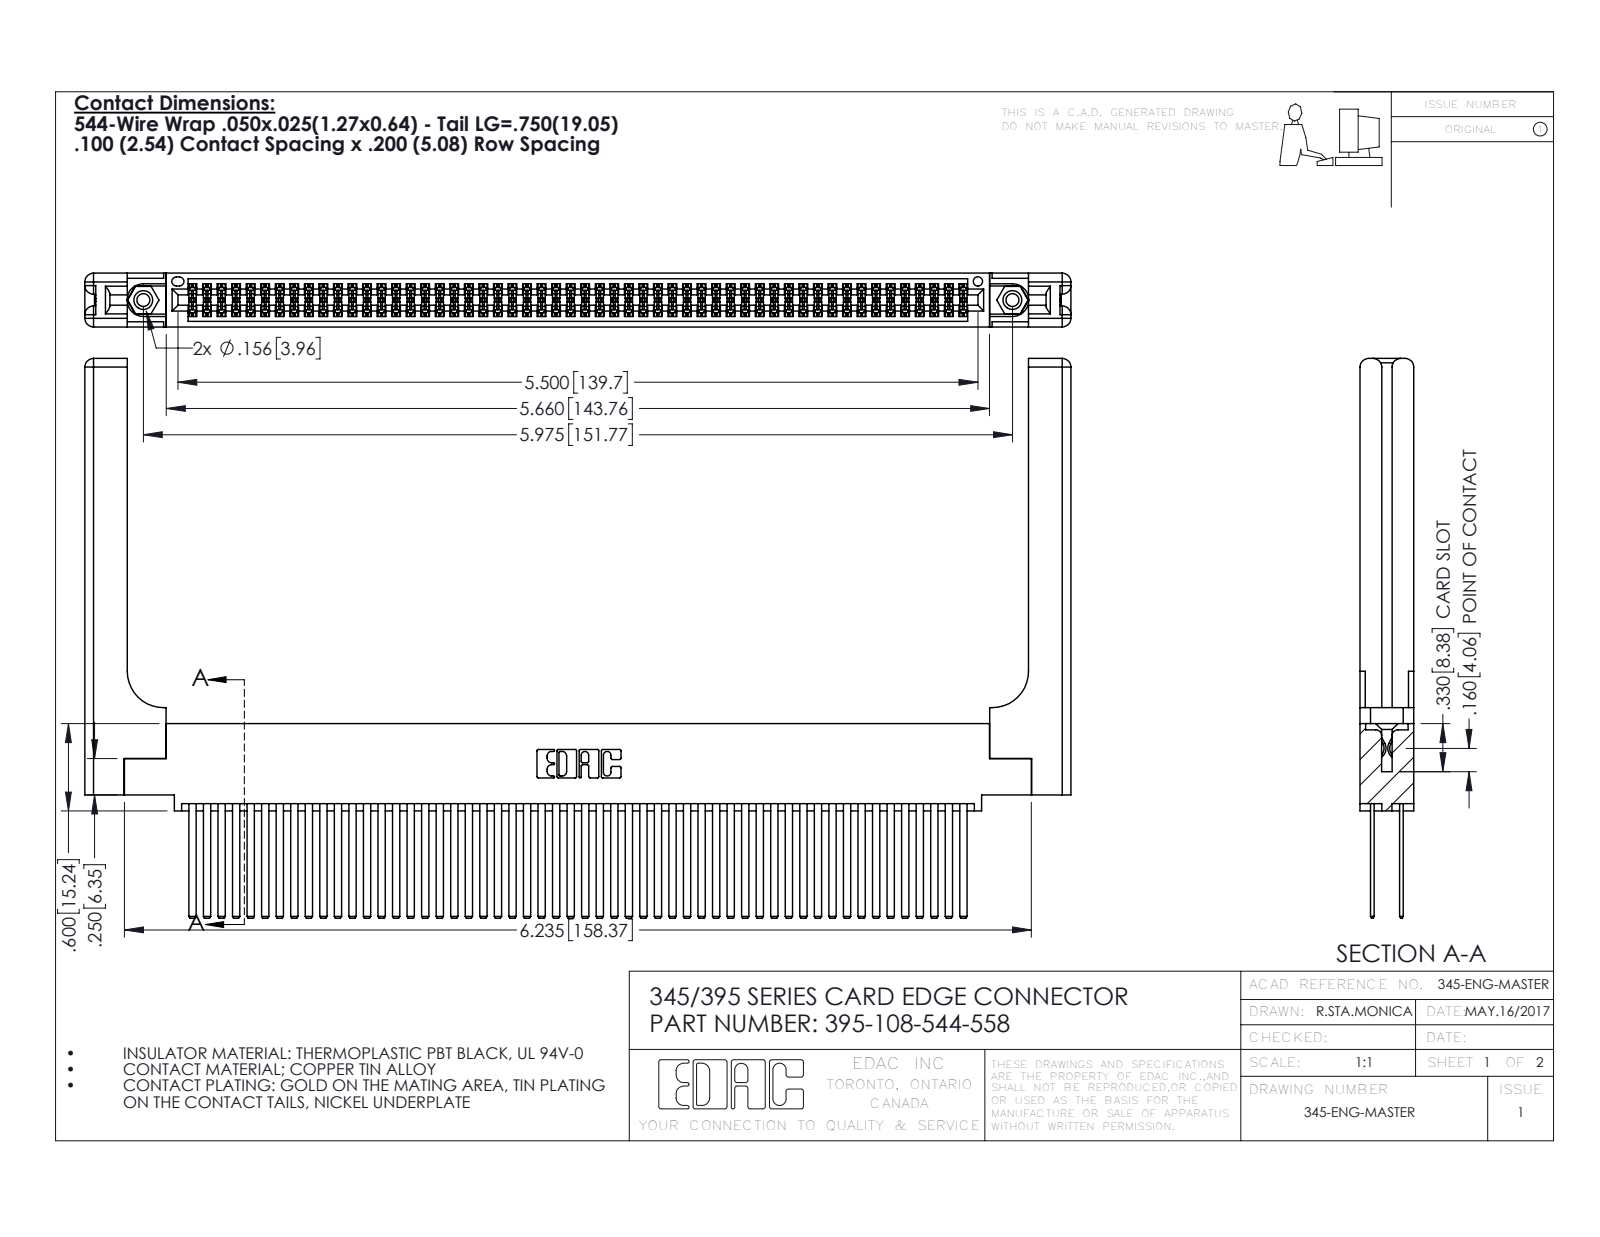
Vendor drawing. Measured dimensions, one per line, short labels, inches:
name: 345-220-058_345-220-058; 395-108-544-558; 345-292-001_345-293-144; 345-250-001_345-250-001-102 (+1 more)
written by: SolidWorks 2016 (CONFIG_CONTROL_DESIGN)
unit: in
bodies: 113 solids, 5138 faces (3364 planar, 1714 cylindrical, 60 other)
size: 6.779 × 3.847 × 0.37
volume: 1.633 in³; area: 57.1 in²
holes: 2× ⌀0.089, 2× ⌀0.125, 2× ⌀0.156, 1× ⌀0.064
bosses: 2× ⌀0.155
rounds: 162× R0.006, 22× R0.01, 16× R0.06, 6× R0.007, 6× R0.031, 3× R0.026, 2× R0.014, 2× R0.019
face distances: 0.072, 0.298, 0.098, 0.272, 0.025, 0.2, 0.37, 0.225, 0.175, 0.148
hole spacings: 0.27, 5.739, 5.975
